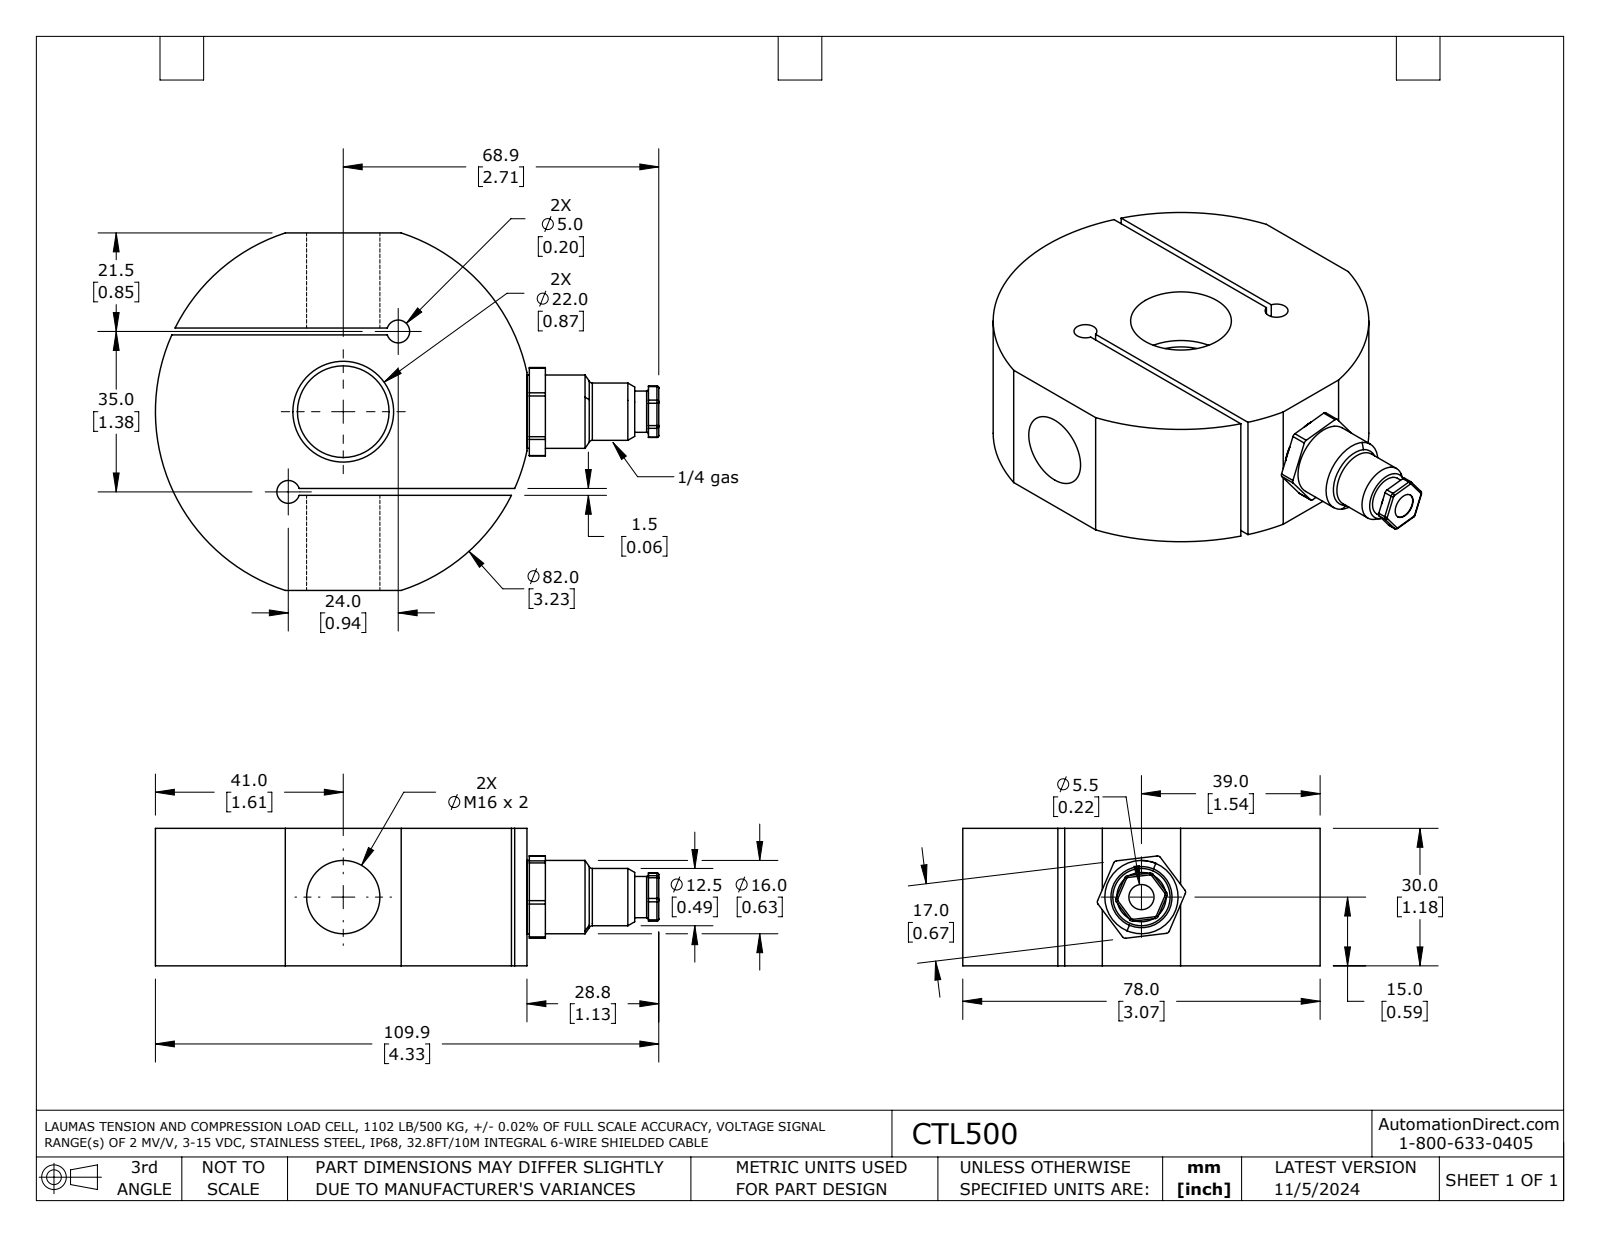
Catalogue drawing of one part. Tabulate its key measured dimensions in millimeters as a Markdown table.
| quantity | value |
| --- | --- |
| part name | CTL500 |
| STEP written by | SolidWorks 2021 (AUTOMOTIVE_DESIGN) |
| units | millimeters |
| bodies | 2 solids, 102 faces (32 planar, 51 cylindrical, 19 other) |
| overall size | 109.9 × 78 × 30 |
| volume | 134 100 mm³ |
| surface area | 29 590 mm² |
| round holes (diameter × count) | 5 × 2, 5.5 × 1, 14 × 1, 16 × 1, 22 × 1 |
| round bosses / shafts (diameter × count) | 16 × 1, 12.5 × 1, 9 × 1 |
| partial cylindrical surfaces (radius × count) | 0.8 × 12, 0.4 × 6, 41 × 1 |
| main face-to-face distances | 30, 1.5, 35, 33.5, 36.5, 20.8, 22.3, 55.8, 57.3, 14 |
| hole center spacings | 21.2, 42.4 |
